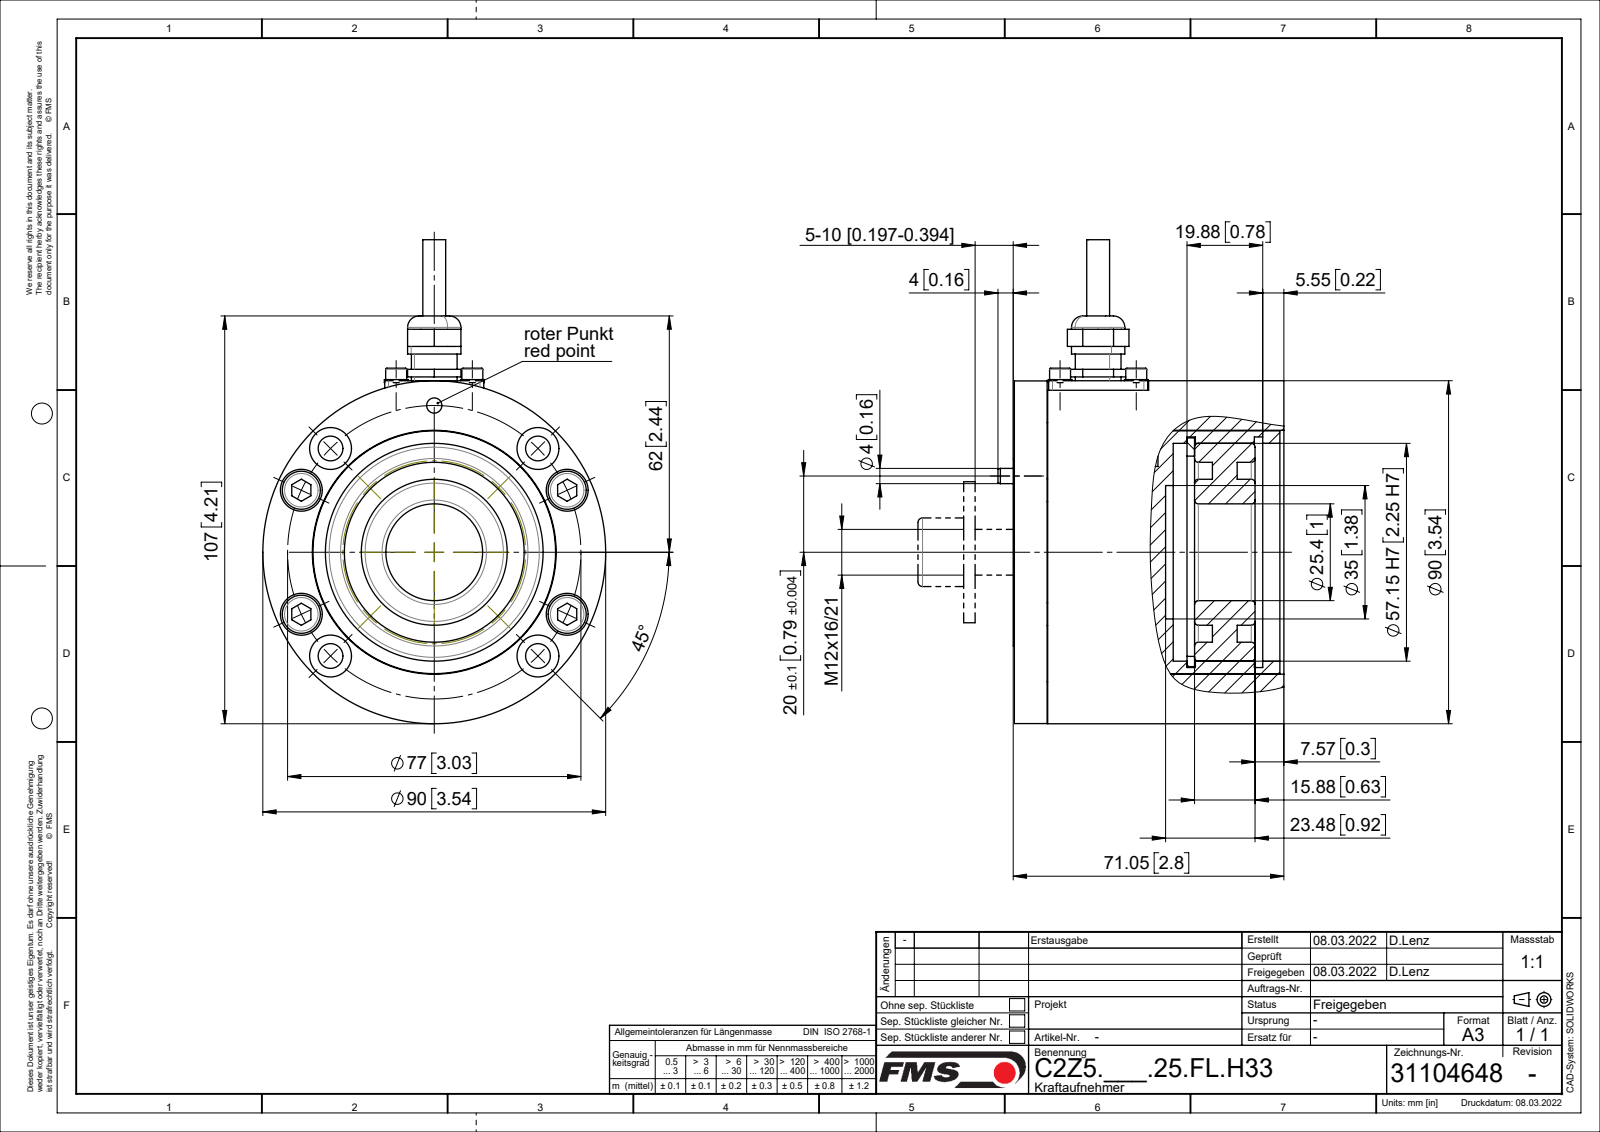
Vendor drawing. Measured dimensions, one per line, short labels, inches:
name: Zyl-Schr DIN912_M6x30; Spannstift_ISO13337_D04x10; PKL_NLJ1_vereinfacht_01; Zyl-Schr DIN912_M3x6 (+8 more)
written by: SolidWorks 2018 (CONFIG_CONTROL_DESIGN)
unit: in
bodies: 23 solids, 525 faces (201 planar, 228 cylindrical, 96 other)
size: 5 × 3.781 × 3.543
volume: 18.78 in³; area: 186.8 in²
holes: 8× ⌀0.256, 8× ⌀0.433, 6× ⌀0.098, 4× ⌀0.122, 4× ⌀0.134, 4× ⌀0.197, 4× ⌀0.276, 2× ⌀0.157, 1× ⌀0.118, 1× ⌀0.236, 1× ⌀0.402, 1× ⌀0.48
bosses: 4× ⌀0.394, 4× ⌀0.244, 4× ⌀0.236, 4× ⌀0.217, 4× ⌀0.118, 2× ⌀0.472, 1× ⌀3.543, 1× ⌀3.539
rounds: 4× R0.004, 4× R0.039, 2× R0.02, 2× R0.164, 2× R0.197, 1× R0.913, 1× R1.035
face distances: 0.236, 1.301, 1.26, 1.496, 0.339, 1.146, 1.484, 0.224, 0.114, 1.14
hole spacings: 0.787, 1.516, 0.526, 0.557, 1.515, 1.739, 2.143, 2.483
